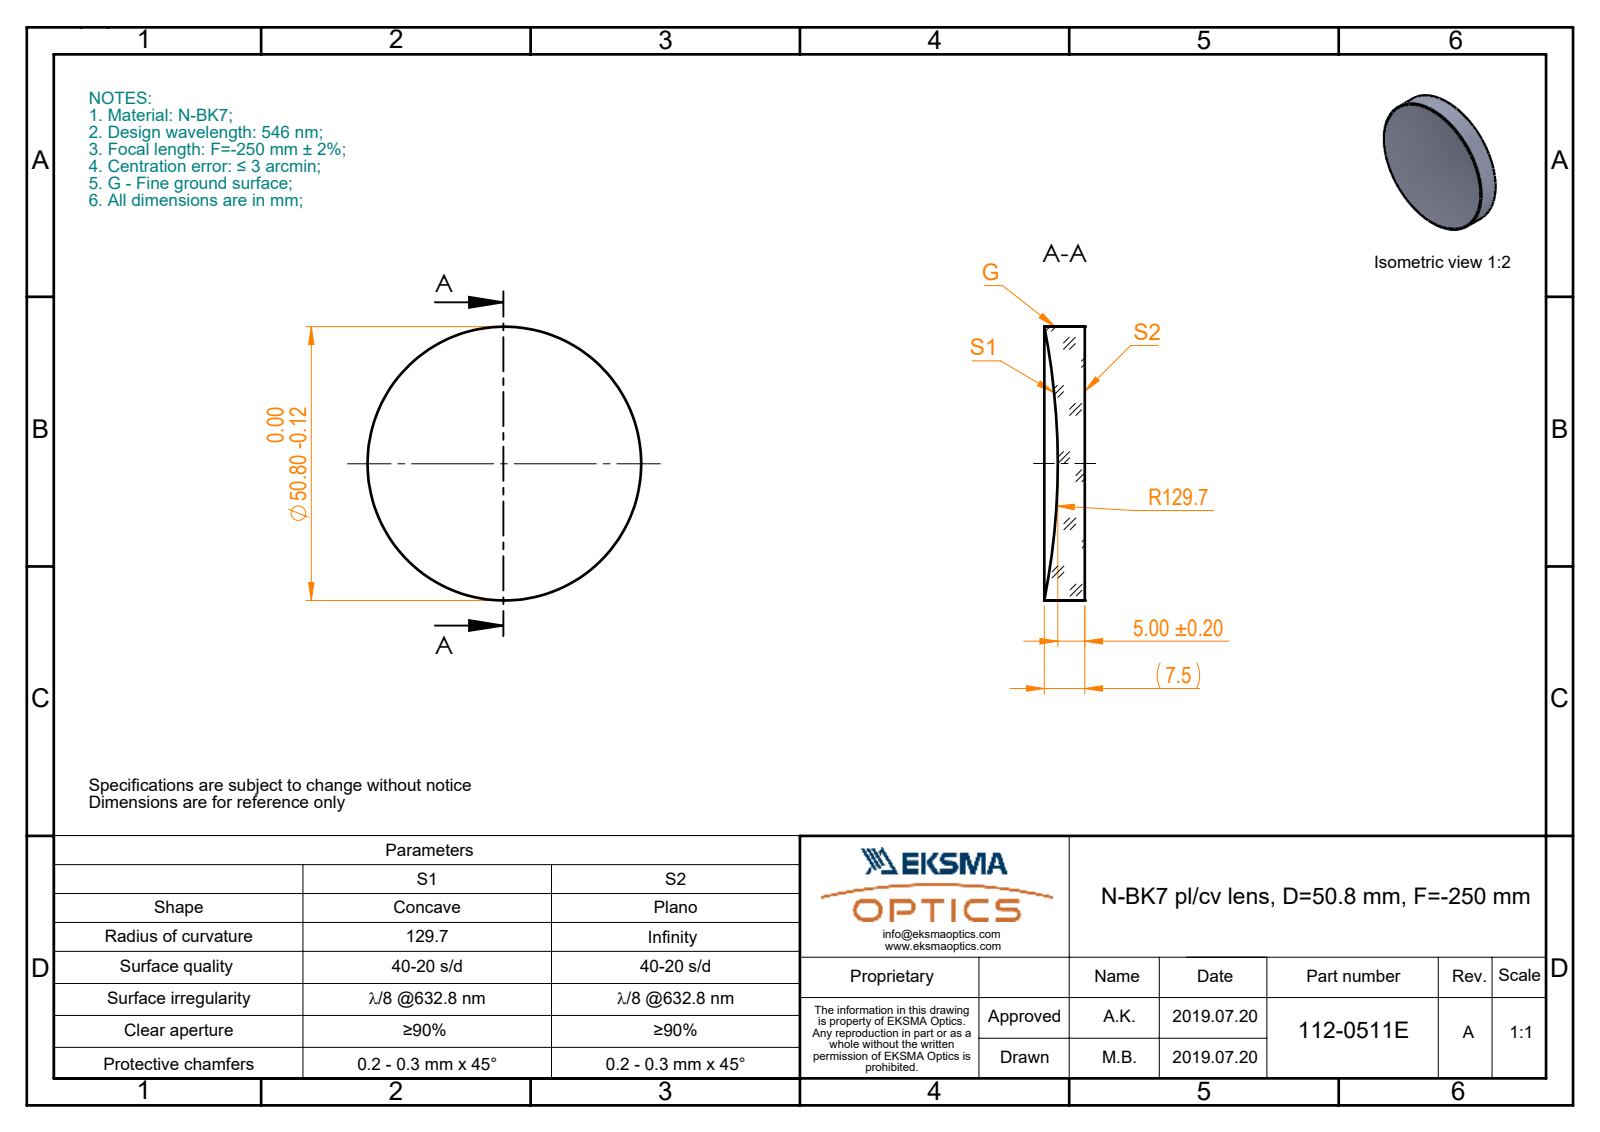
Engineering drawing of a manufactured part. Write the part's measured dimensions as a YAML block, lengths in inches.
part_name: "112-0511 BK7 pl-cv 50.8 F-250"
step_written_by: "SolidWorks 2017 (CONFIG_CONTROL_DESIGN)"
units: inches
bodies: {solids: 1, faces: 5, planar: 1, cylindrical: 2, other: 2}
overall_size: [2, 2, 0.296]
volume: 0.773
surface_area: 8.172
round_bosses_or_shafts:
  - {diameter: 2, count: 1}
